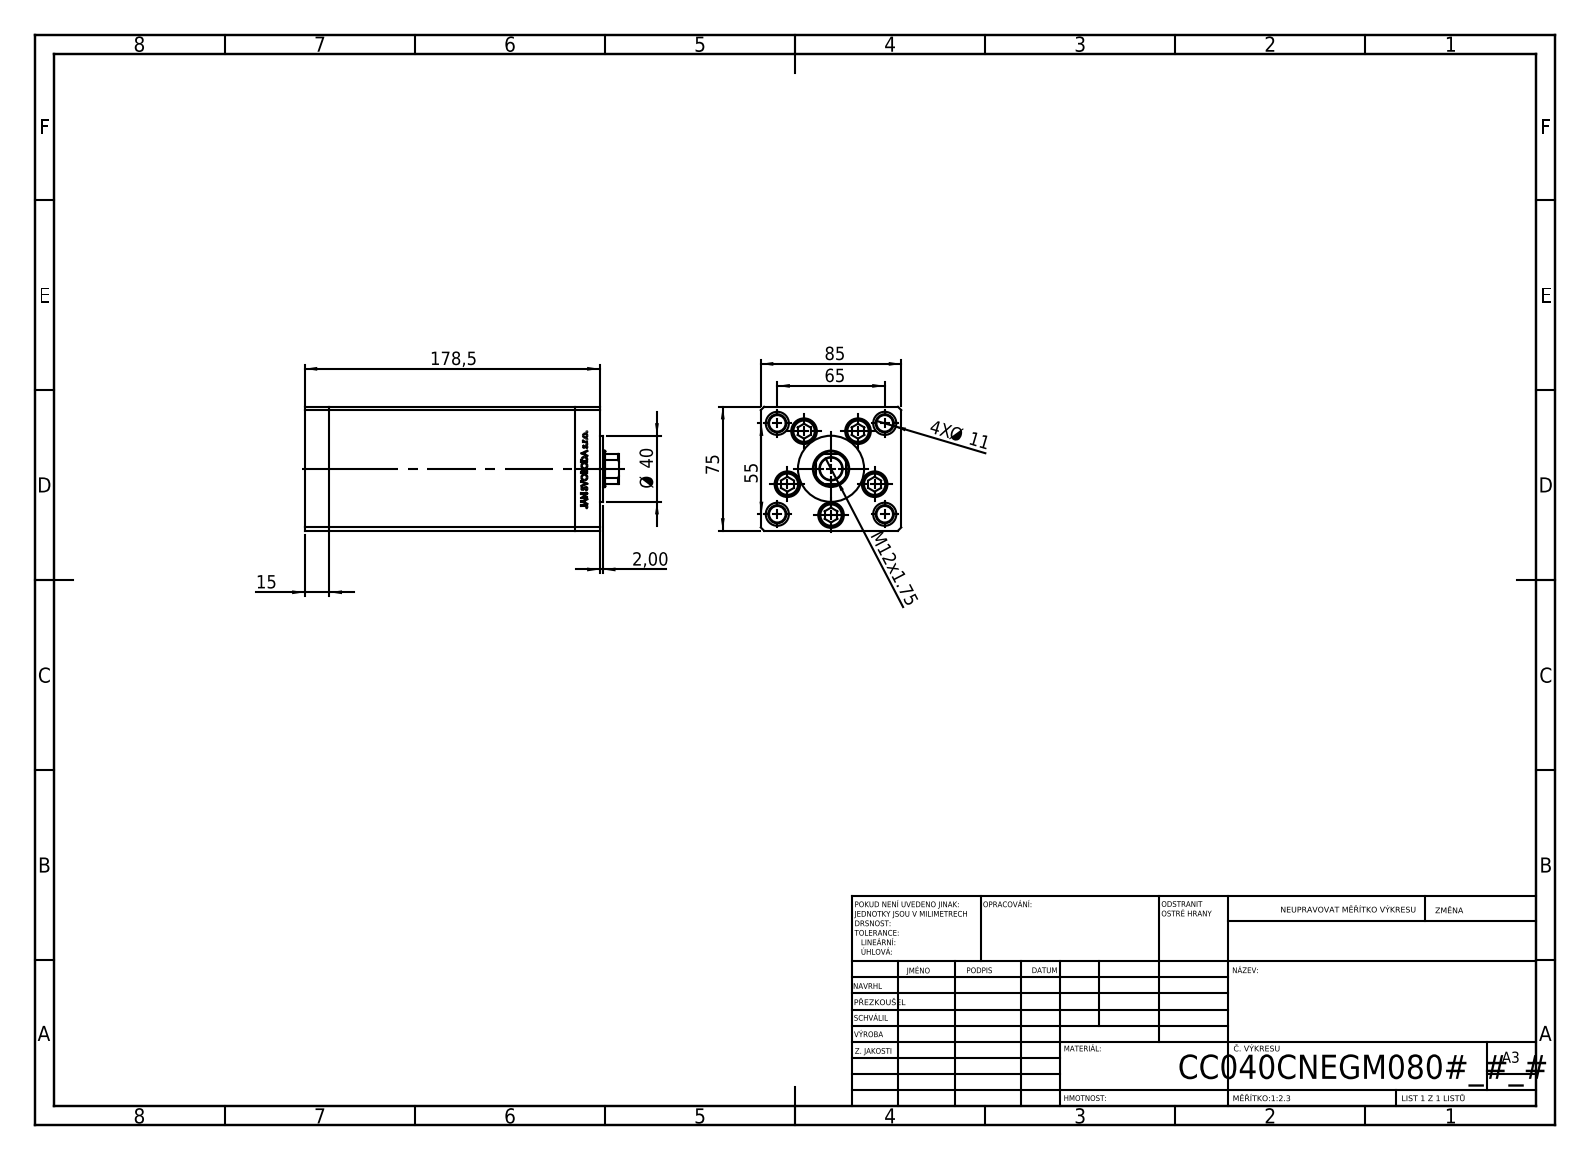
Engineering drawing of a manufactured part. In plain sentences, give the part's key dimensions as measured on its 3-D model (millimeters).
The part is named "ALLEN BOLT; V220C BACK_C; V220C FRONT; V220C_C MIDDLE (+1 more)". Its 3-D file was written by "SolidWorks 2019 (CONFIG_CONTROL_DESIGN)". It is 13 solids with 1159 faces: 538 planar, 159 cylindrical and 462 other. Overall it measures 190 by 85 by 75 millimeters. Its volume is 949 001 cubic millimeters and its surface area 179 253 square millimeters. Round holes: 9 of diameter 11, 5 of diameter 15.5, 4 of diameter 10, 4 of diameter 14, 1 of diameter 13.5, 1 of diameter 14.5, 1 of diameter 22. Round bosses or shafts: 5 of diameter 8, 4 of diameter 14.5, 1 of diameter 40. Partial cylindrical surfaces (rounded edges, fillets, slot ends): 2 of radius 0.93, 1 of radius 10.5. The main face-to-face distances are 85, 75, 15, 148.5, 163.5, 10.5, 178.5, 34.25, 144.25, 129.25. The hole center spacings are 28, 42.57, 16.86, 19.17, 32.33, 32.5, 33.63, 37.33.
